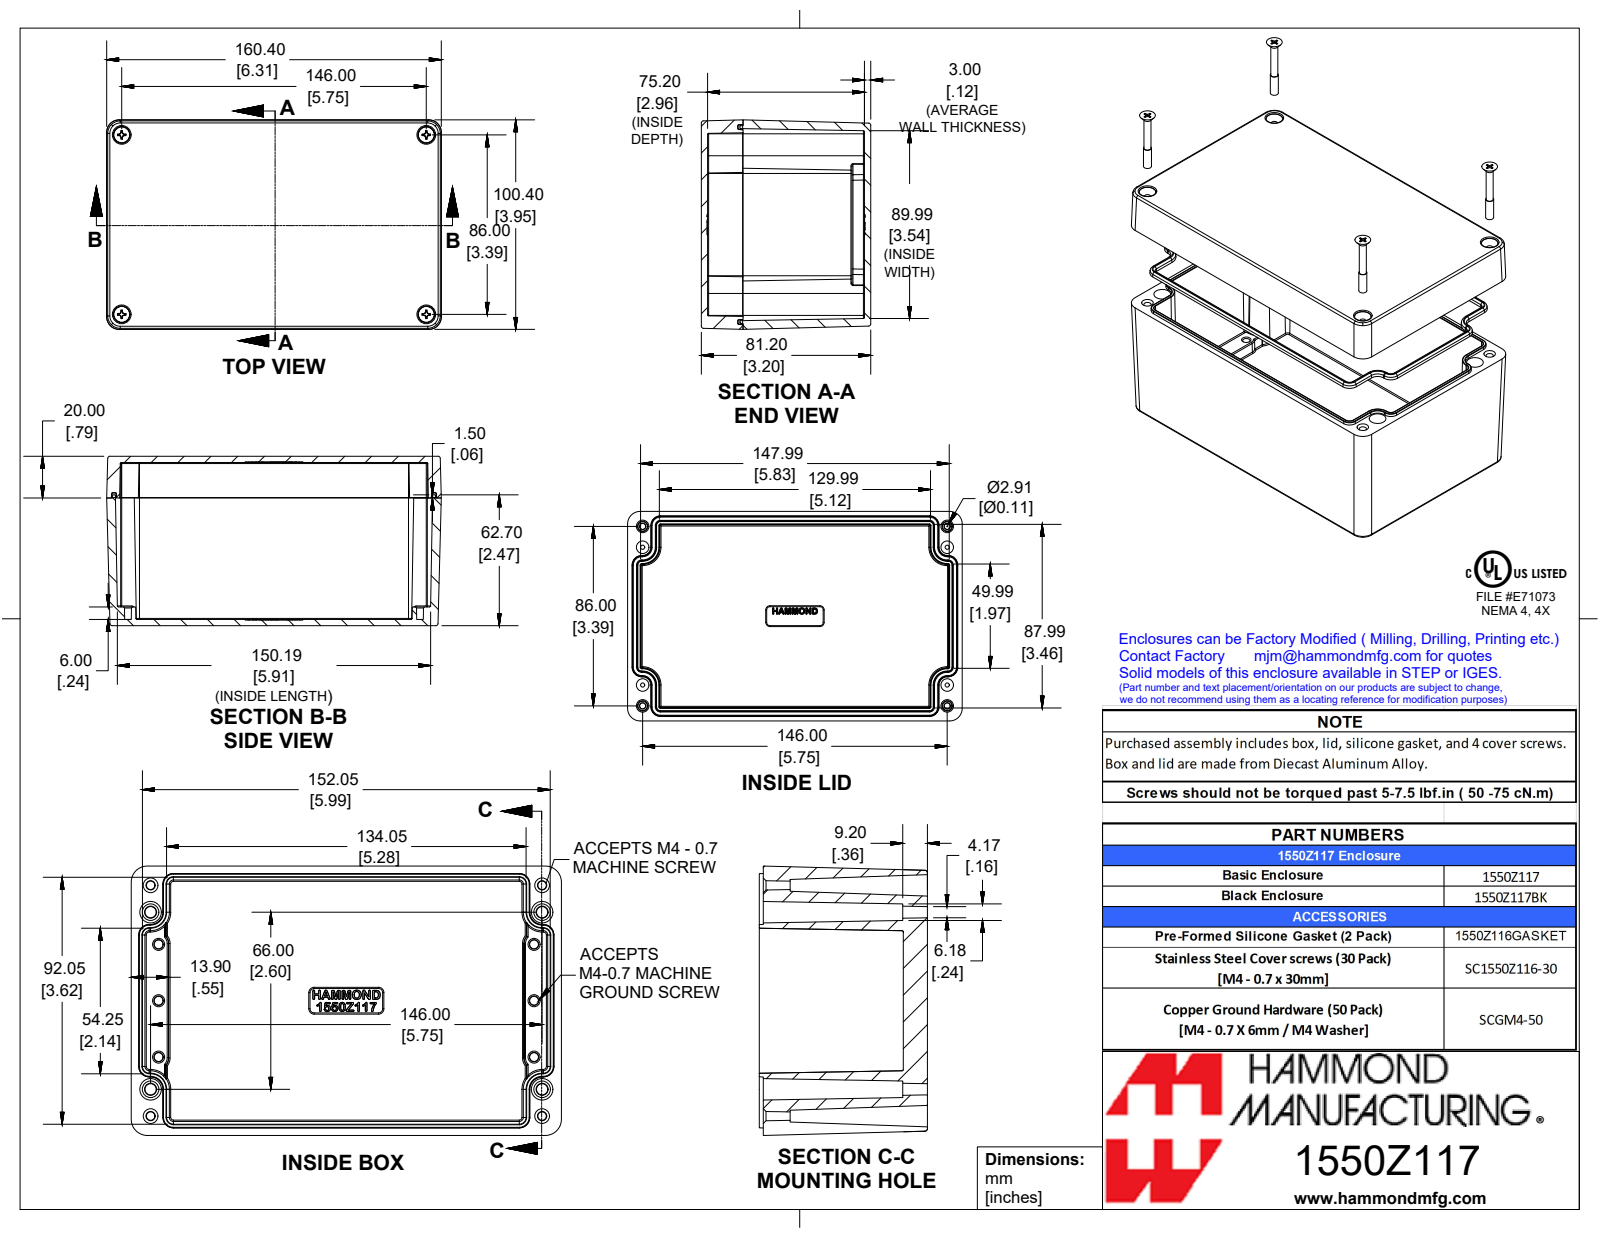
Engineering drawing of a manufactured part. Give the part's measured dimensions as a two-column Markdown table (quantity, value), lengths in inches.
| quantity | value |
| --- | --- |
| part name | 1550Z117 |
| STEP written by | SolidWorks 2019 (AUTOMOTIVE_DESIGN) |
| units | inches |
| bodies | 7 solids, 1289 faces (357 planar, 240 cylindrical, 692 other) |
| overall size | 6.315 × 3.953 × 3.197 |
| volume | 18.07 in³ |
| surface area | 244.8 in² |
| round bosses / shafts (diameter × count) | 0.299 × 4, 0.154 × 4, 0.13 × 4 |
| partial cylindrical surfaces (radius × count) | 0.008 × 40, 0.02 × 32, 0.039 × 24, 0.012 × 16, 0.236 × 8, 0.157 × 4 |
| main face-to-face distances | 0.118, 3.079, 3.197, 2.961, 3.953, 3.543, 0.354, 0.669, 0.787, 2.409 |
